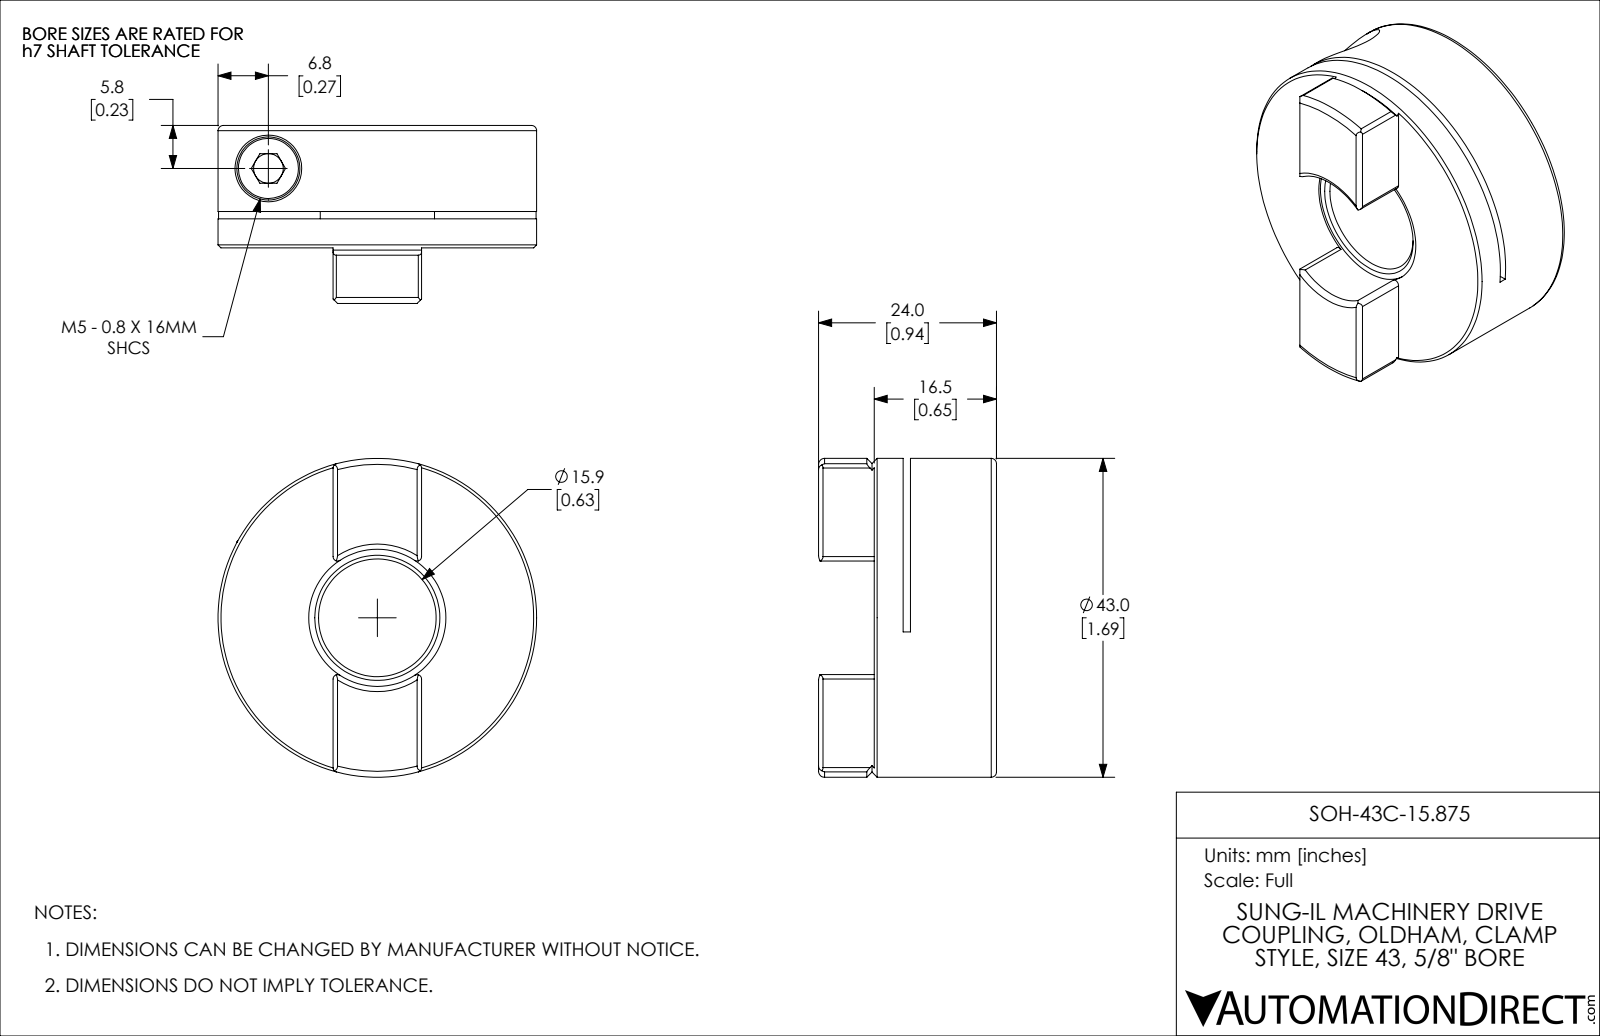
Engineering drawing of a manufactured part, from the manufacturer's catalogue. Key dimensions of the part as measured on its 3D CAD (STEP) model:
Part name (STEP PRODUCT): SOH-43C-15.875
STEP written by: SolidWorks 2021 (CONFIG_CONTROL_DESIGN)
Units: inches
Bodies: 2 solids, 97 faces (39 planar, 33 cylindrical, 25 other)
Overall size (bounding box): 1.693 × 1.693 × 0.945
Volume: 1.314 in³ · Surface area: 13.67 in²
Round holes (diameter × count): ⌀0.157 ×1, ⌀0.165 ×1, ⌀0.213 ×1, ⌀0.354 ×1, ⌀0.625 ×1, ⌀0.728 ×1
Round bosses / shafts (diameter × count): ⌀1.693 ×1, ⌀0.335 ×1, ⌀0.197 ×1
Partial cylindrical surfaces — rounded edges, fillets, slot ends (radius × count): R0.024 ×8, R1.476 ×1
Main face-to-face distances: 0.65, 0.496, 0.154, 0.457, 0.039, 0.193, 0.488, 0.945, 0.449, 0.295
